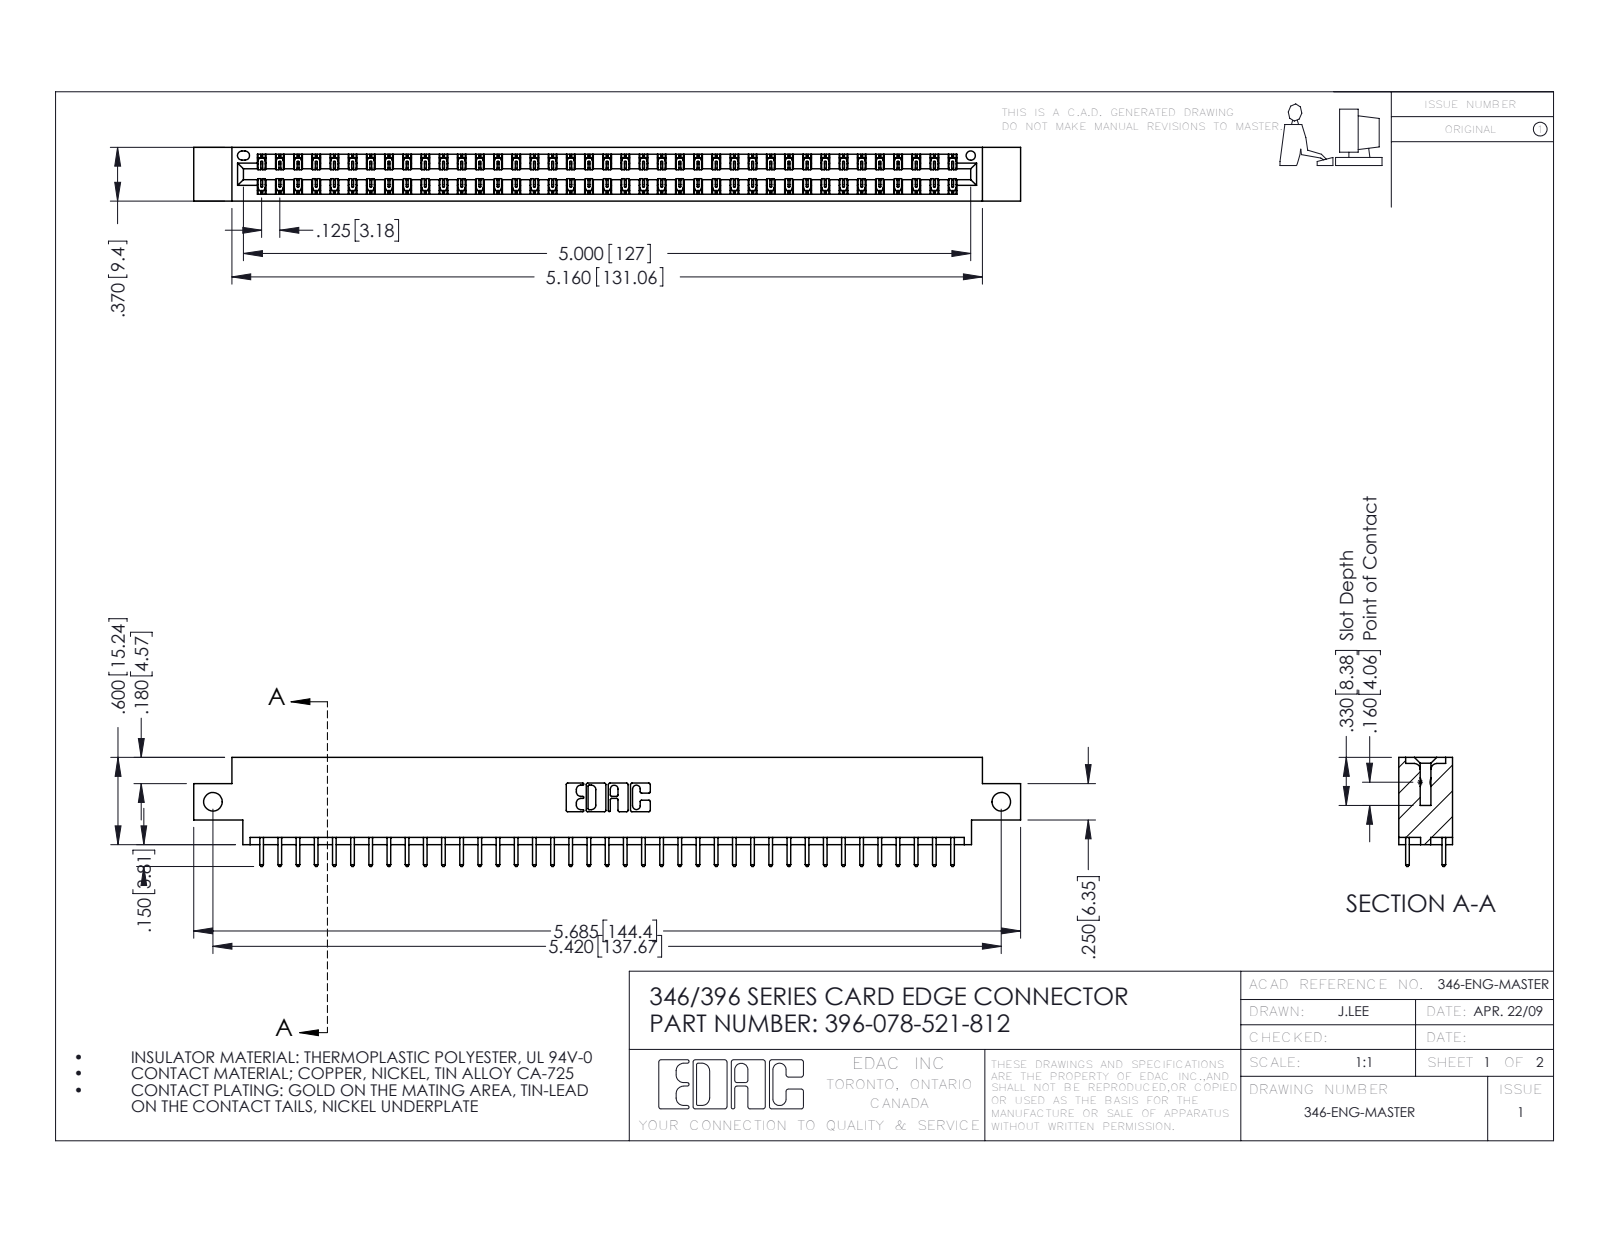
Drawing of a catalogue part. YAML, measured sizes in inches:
part_name: "346 Part_0.170 Offset - Side Mount; 345-292-001_345-293-121; 396-078-521-812"
step_written_by: "SolidWorks 2016 (CONFIG_CONTROL_DESIGN)"
units: inches
bodies: {solids: 79, faces: 4182, planar: 2810, cylindrical: 1372, other: 0}
overall_size: [5.685, 0.75, 0.37]
volume: 0.841
surface_area: 29.03
round_holes:
  - {diameter: 0.128, count: 2}
  - {diameter: 0.064, count: 1}
partial_cylinders:
  - {radius: 0.006, count: 117}
  - {radius: 0.01, count: 78}
  - {radius: 0.01, count: 22}
  - {radius: 0.007, count: 6}
  - {radius: 0.031, count: 6}
  - {radius: 0.026, count: 3}
  - {radius: 0.014, count: 2}
  - {radius: 0.022, count: 2}
face_to_face_distances: [0.048, 0.322, 0.37, 0.25, 0.072, 0.298, 0.025, 0.275, 0.148, 0.222]
hole_center_spacings: [5.42]
